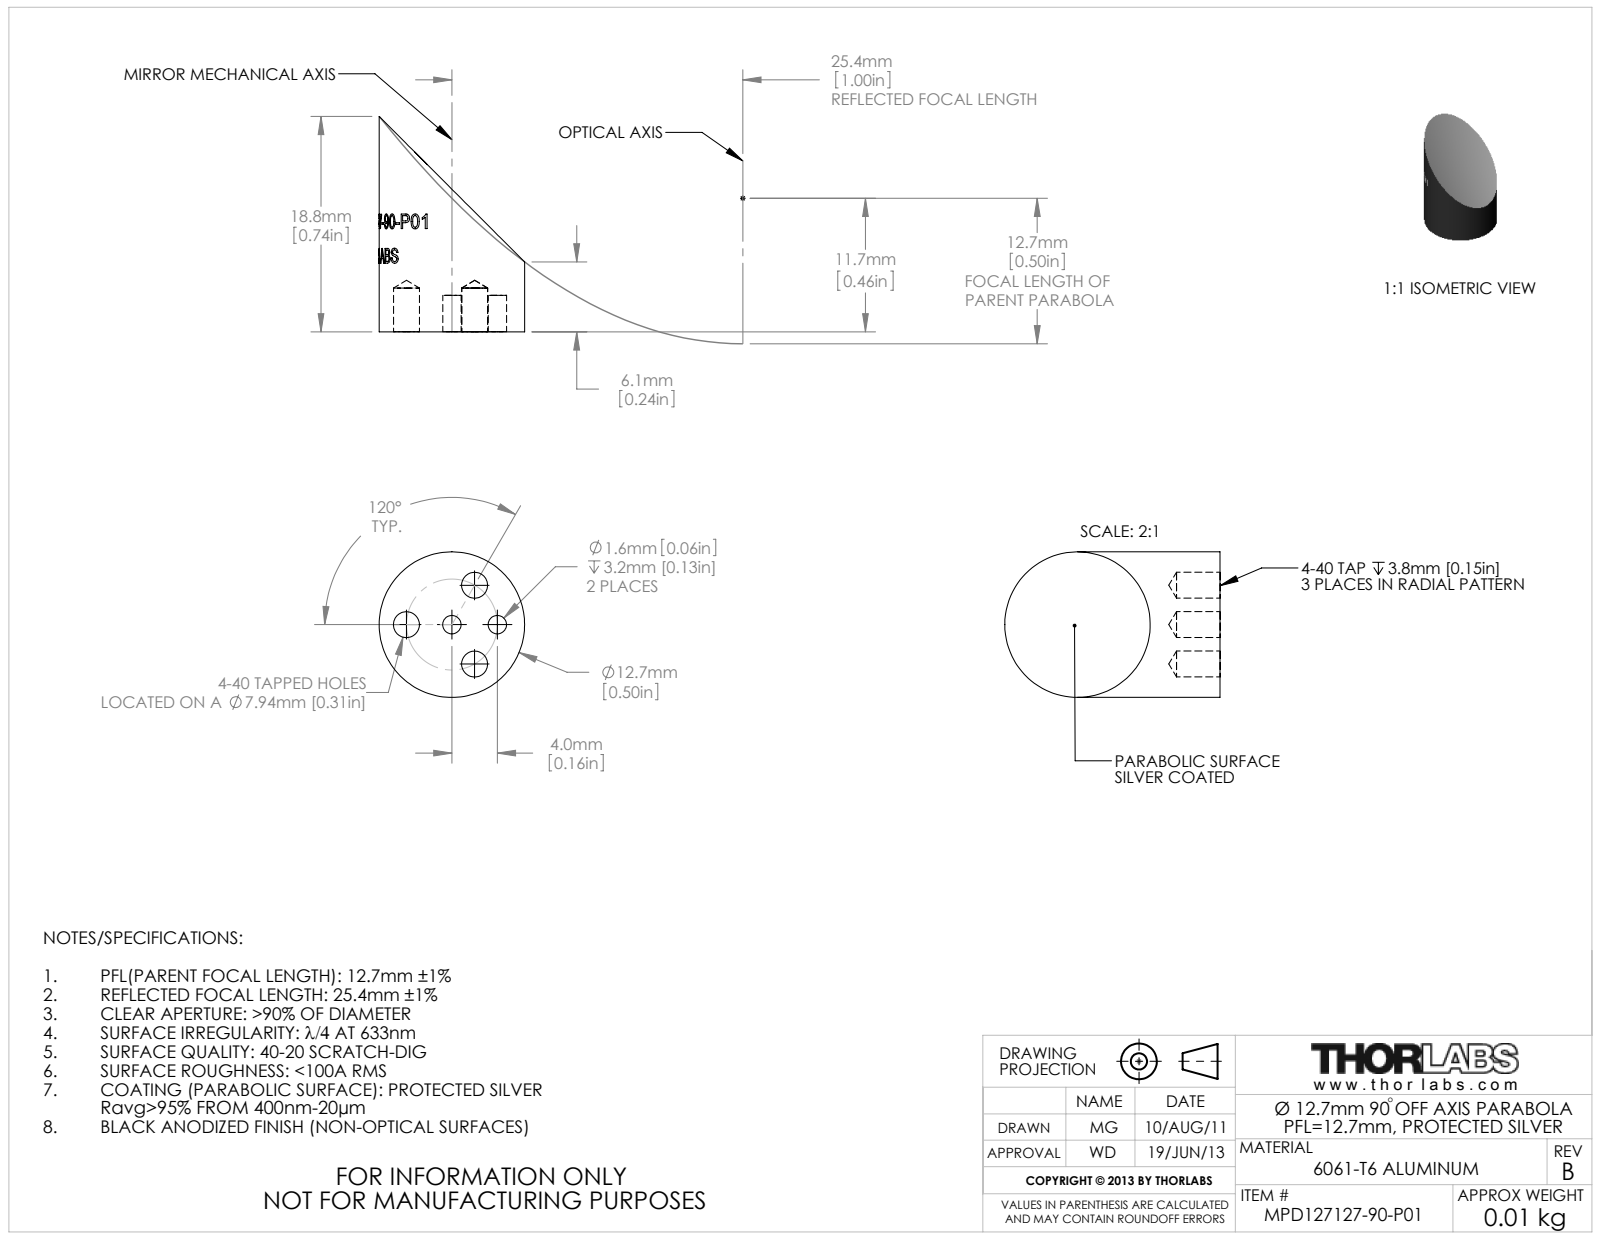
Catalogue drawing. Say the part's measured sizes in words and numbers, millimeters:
The part is named "22875-E0W". Its 3-D file was written by "SolidWorks 2011 (AUTOMOTIVE_DESIGN)". It is 0 solids with 50 faces: 1 planar, 47 cylindrical and 2 other. Overall it measures 18.8 by 12.7 by 12.7 millimeters. Round holes: 3 of diameter 2.26, 2 of diameter 1.6. Round bosses or shafts: 1 of diameter 12.7. The hole center spacings are 3.97, 6.87, 6.88, 7.94.
